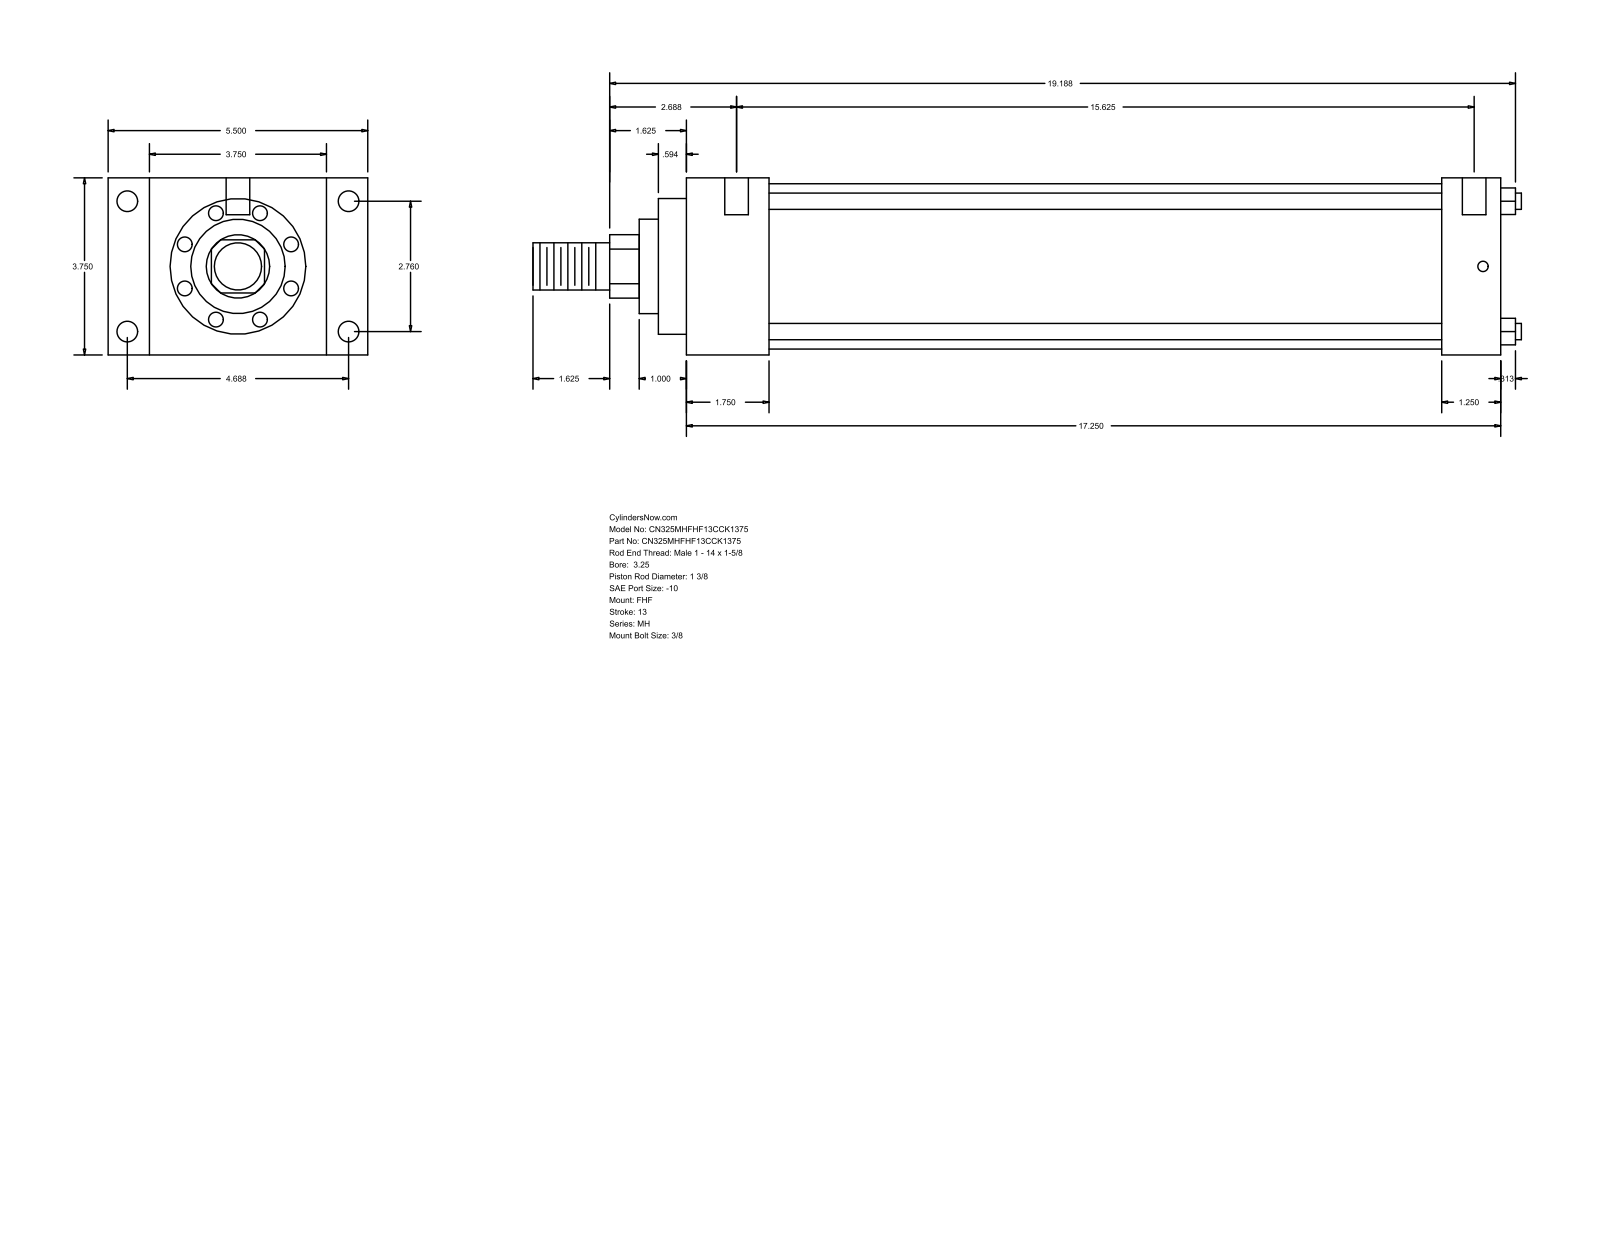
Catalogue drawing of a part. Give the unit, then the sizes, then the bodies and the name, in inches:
Units: inches
Overall size (bounding box): 20.937 × 5.5 × 3.75
Round holes (diameter × count): ⌀0.219 ×4, ⌀0.438 ×4, ⌀0.5 ×2
Round bosses / shafts (diameter × count): ⌀0.345 ×4, ⌀3.5 ×1, ⌀2.875 ×1, ⌀2 ×1, ⌀1.375 ×1, ⌀1 ×1
Partial cylindrical surfaces — rounded edges, fillets, slot ends (radius × count): R0.672 ×1
Main face-to-face distances: 3.75, 17.25, 1.75, 15.5, 0.875, 4.625, 5.5, 16, 14.25, 1.25
Hole centre spacings: 2.76, 4.687, 5.439, 15.875, 0.063, 0.187, 15.625, 15.688
Bodies: 0 solids, 90 faces (61 planar, 29 cylindrical, 0 other)
Part name (STEP PRODUCT): MH_FHF__0325_1.375
STEP written by: GSSL Pune (CONFIG_CONTROL_DESIGN)
